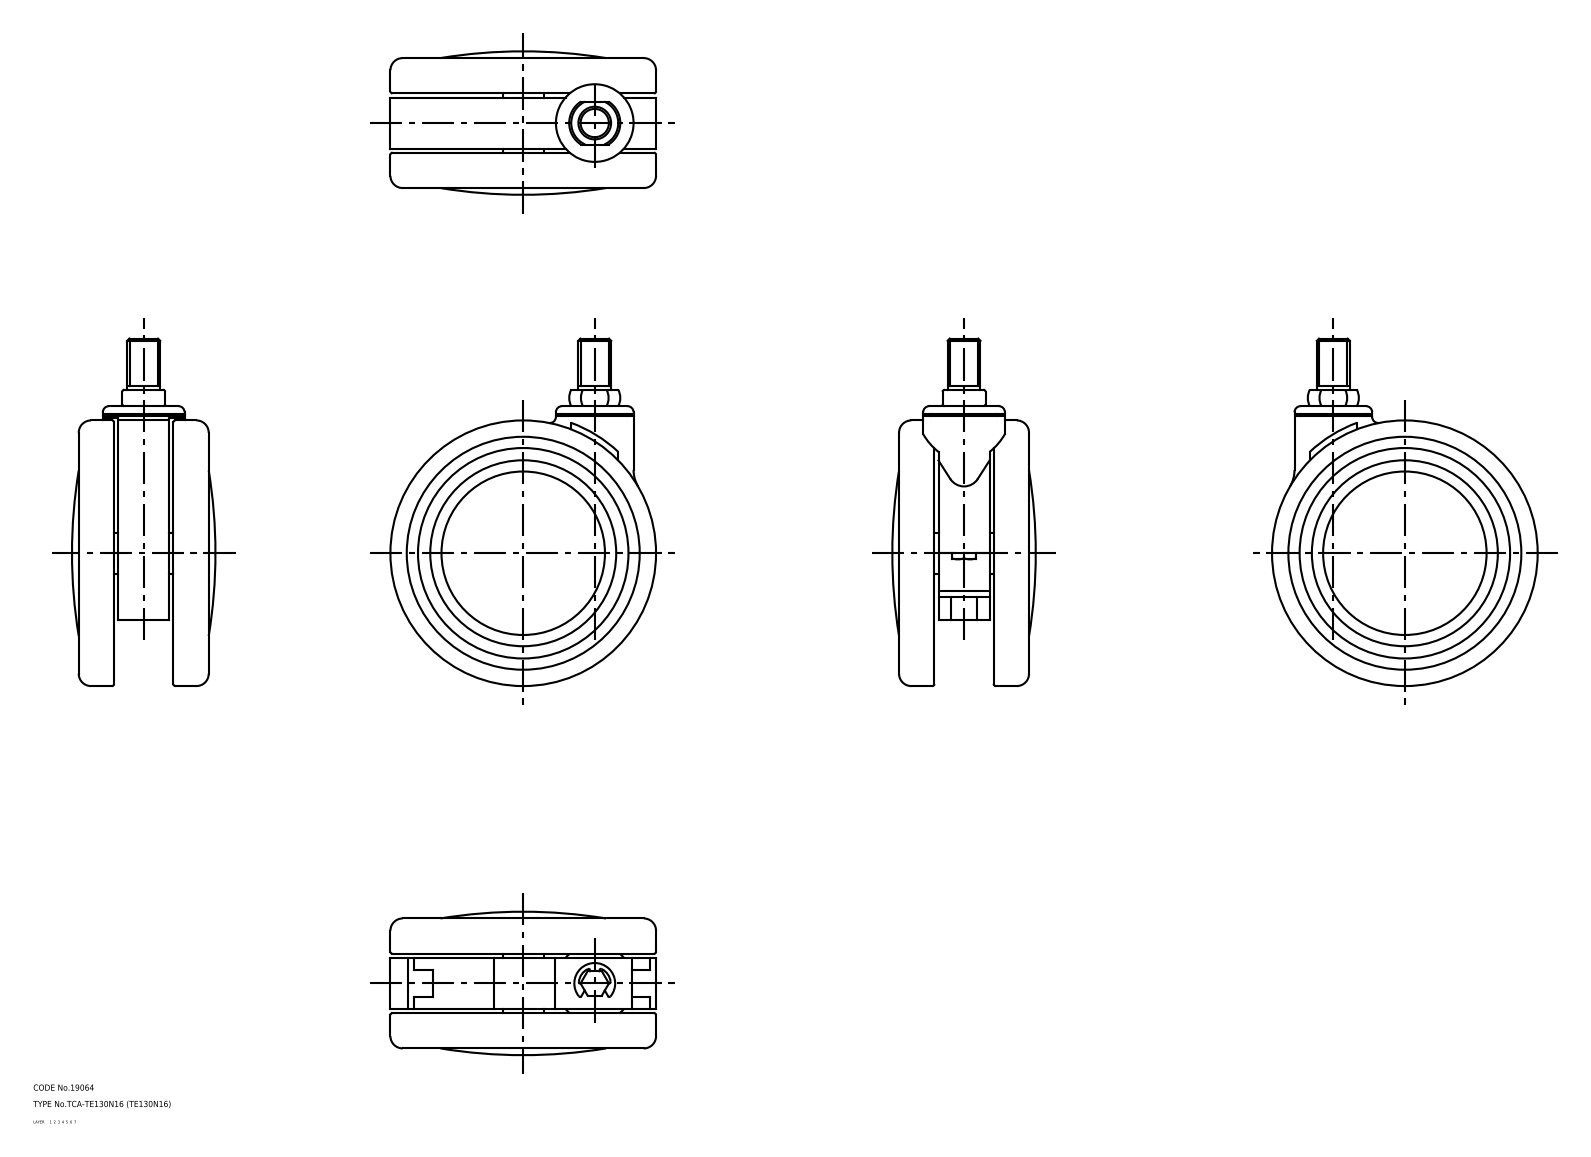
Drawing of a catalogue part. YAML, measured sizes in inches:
part_name: "wheel_mr; wheel; main shaft; TE130N16_5201_36"
step_written_by: "CADfix (AUTOMOTIVE_DESIGN)"
units: inches
bodies: {solids: 4, faces: 158, planar: 0, cylindrical: 0, other: 158}
overall_size: [6.693, 5.118, 2.764]
volume: 36.6
surface_area: 209.2
